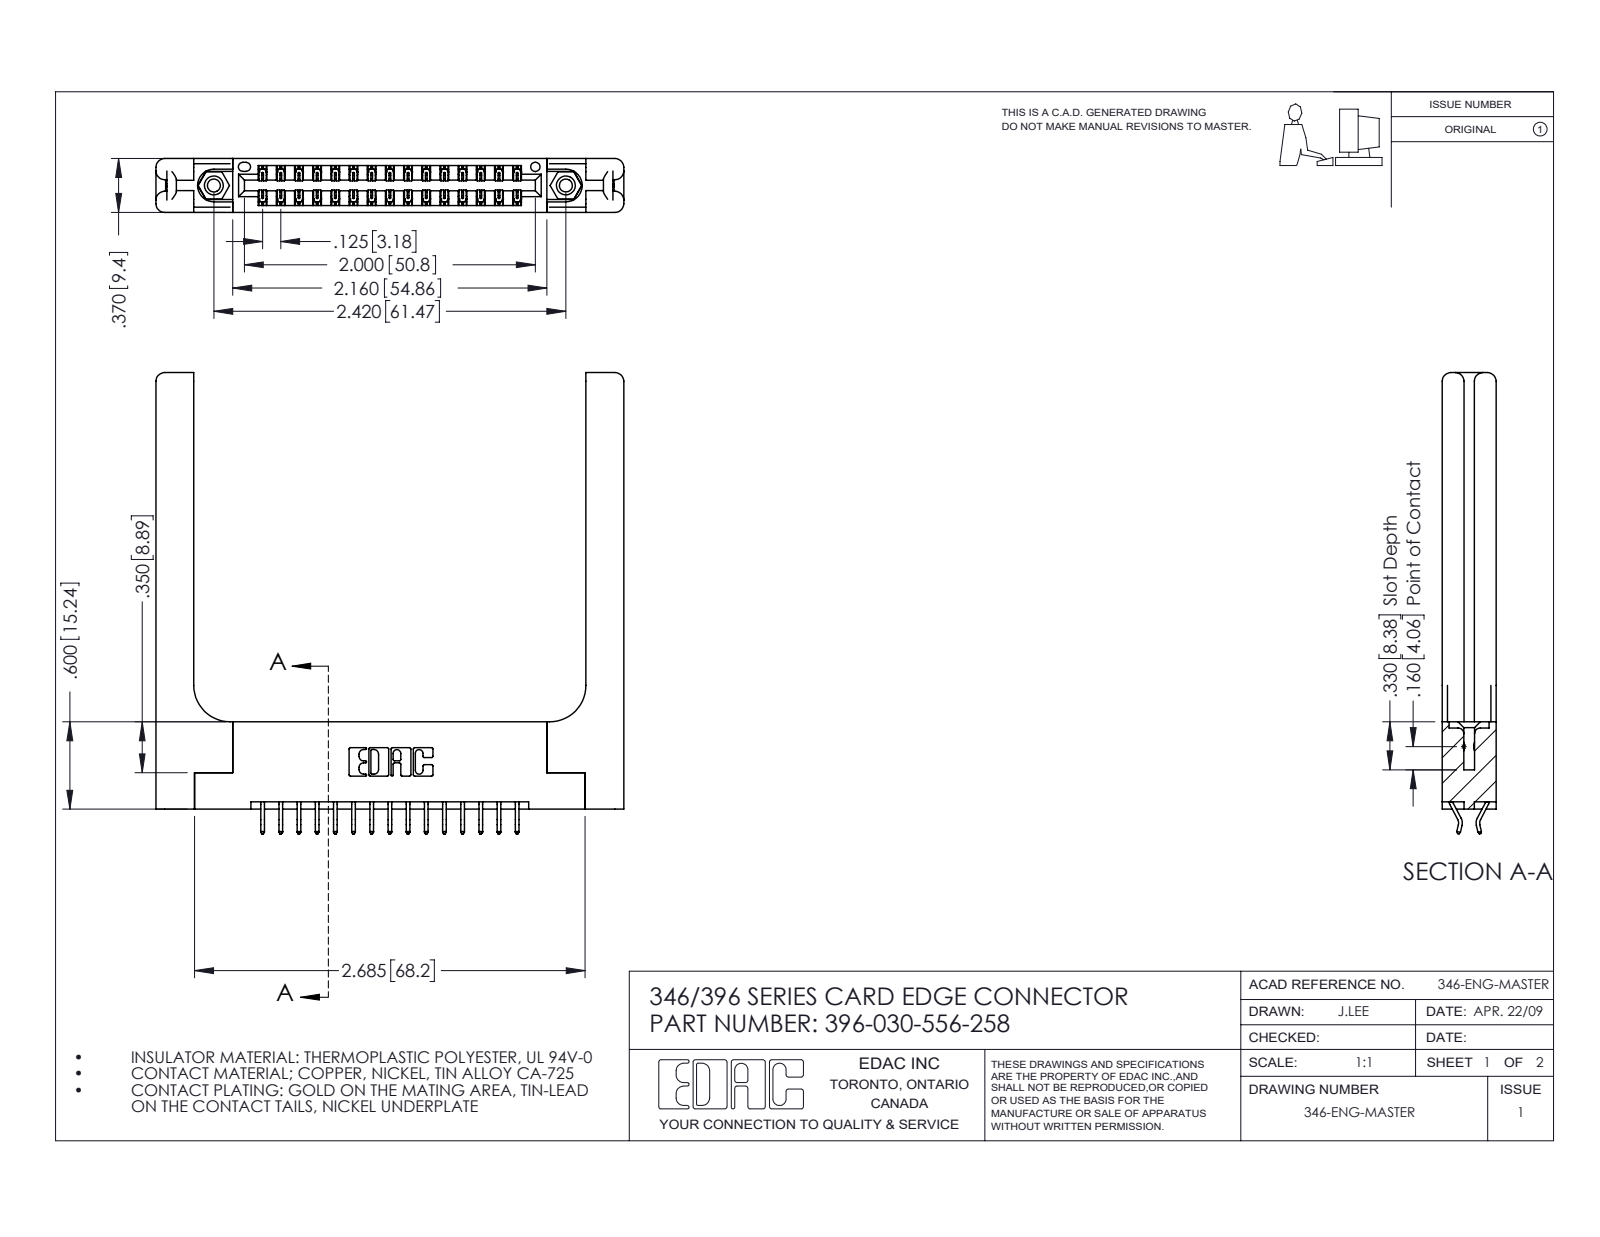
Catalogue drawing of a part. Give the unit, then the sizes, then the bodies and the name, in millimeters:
Units: millimetres
Overall size (bounding box): 81.7 × 80.5 × 9.4
Round holes (diameter × count): ⌀2.3 ×2, ⌀3.2 ×2, ⌀4 ×2, ⌀1.6 ×1
Round bosses / shafts (diameter × count): ⌀3.9 ×2
Partial cylindrical surfaces — rounded edges, fillets, slot ends (radius × count): R0.2 ×45, R0.3 ×22, R1.5 ×16, R0.2 ×6, R0.8 ×6, R0.7 ×3, R0.3 ×2, R0.4 ×2
Main face-to-face distances: 9.4, 3.8, 1.8, 3.8, 1.2, 8.2, 6.4, 2.6, 5.6, 4.4
Hole centre spacings: 6.2, 56.2, 61.5
Volume: 15 300 mm³ · Surface area: 15 180 mm²
Bodies: 35 solids, 2118 faces (1394 planar, 664 cylindrical, 60 other)
Part name (STEP PRODUCT): 346-220-058_345-220-058; 345-292-001_556 Tail; 345-250-001_345-250-001-102; 346 Part_Flush Mounting Lugs - 0.156 Dia-TH (+1 more)
STEP written by: SolidWorks 2016 (CONFIG_CONTROL_DESIGN)
